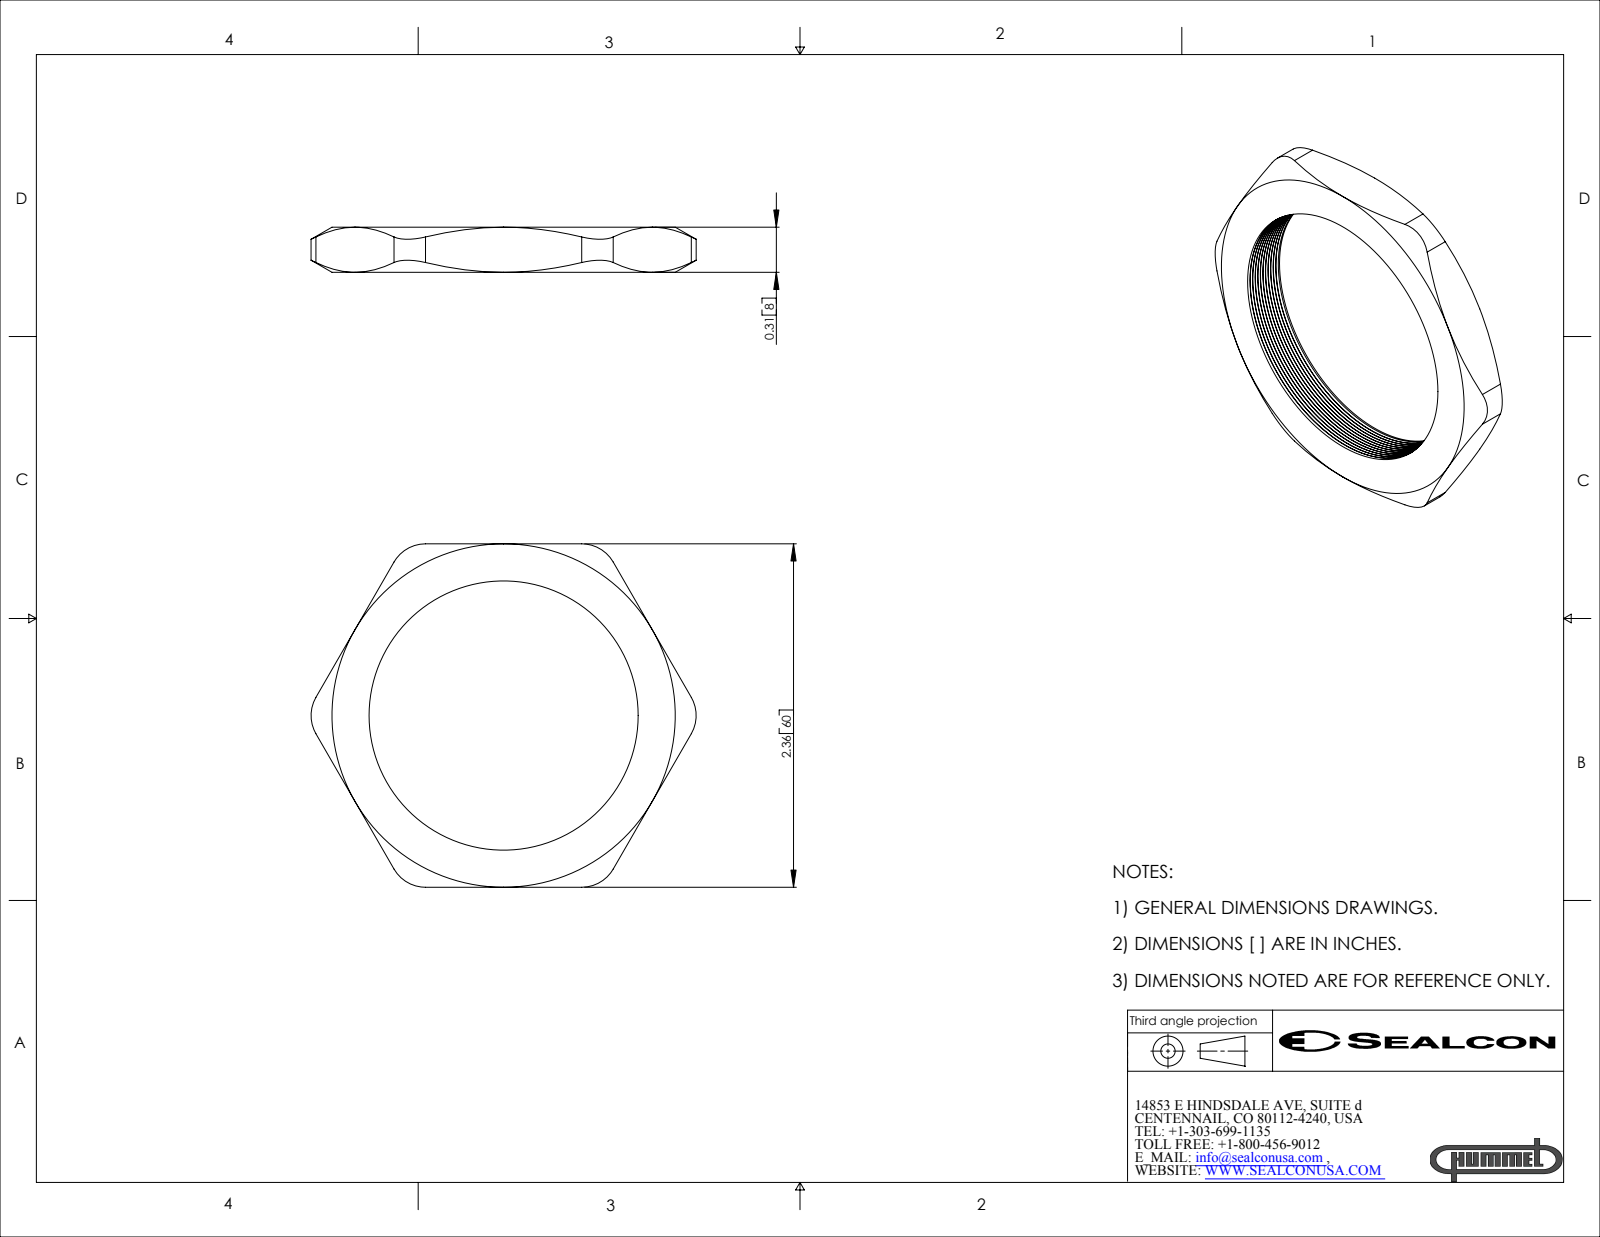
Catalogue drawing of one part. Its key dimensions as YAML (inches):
part_name: "NP-36-GY"
step_written_by: "SolidWorks 2007 (CONFIG_CONTROL_DESIGN)"
units: inches
bodies: {solids: 1, faces: 101, planar: 8, cylindrical: 31, other: 62}
overall_size: [2.648, 2.36, 0.31]
volume: 0.615
surface_area: 9.756
round_holes:
  - {diameter: 1.85, count: 1}
partial_cylinders:
  - {radius: 0.25, count: 6}
face_to_face_distances: [0.31, 2.36]
